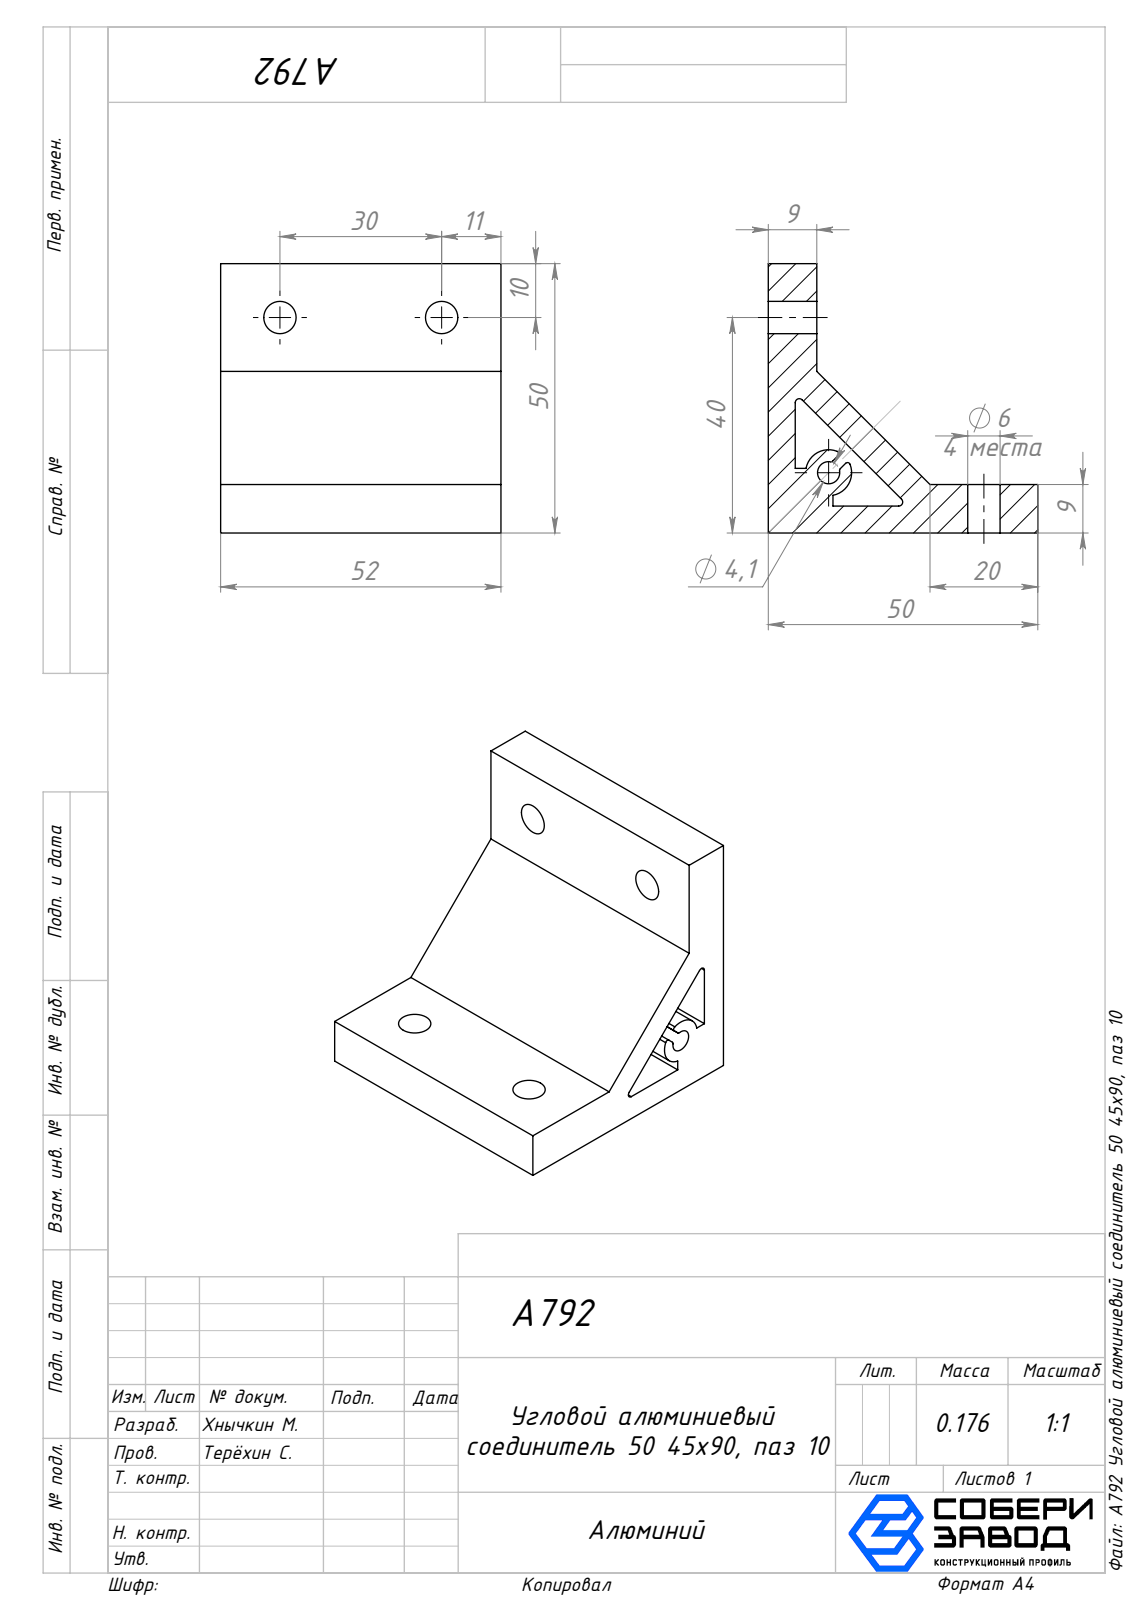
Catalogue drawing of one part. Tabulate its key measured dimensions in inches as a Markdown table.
| quantity | value |
| --- | --- |
| part name | A792 Угловой алюминиевый соединитель 50 45х90, паз 10 |
| STEP written by | SolidWorks 2025 (AUTOMOTIVE_DESIGN) |
| units | inches |
| bodies | 1 solid, 38 faces (16 planar, 22 cylindrical, 0 other) |
| overall size | 2.047 × 1.969 × 1.969 |
| volume | 2.752 in³ |
| surface area | 25.76 in² |
| round holes (diameter × count) | 0.236 × 4, 0.162 × 1 |
| partial cylindrical surfaces (radius × count) | 0.02 × 4, 0.03 × 2, 0.168 × 1 |
| main face-to-face distances | 0.354, 0.222, 0.197, 0.157, 1.969, 1.772, 1.614, 2.047, 0.472, 0.276 |
| hole center spacings | 1.181 |
